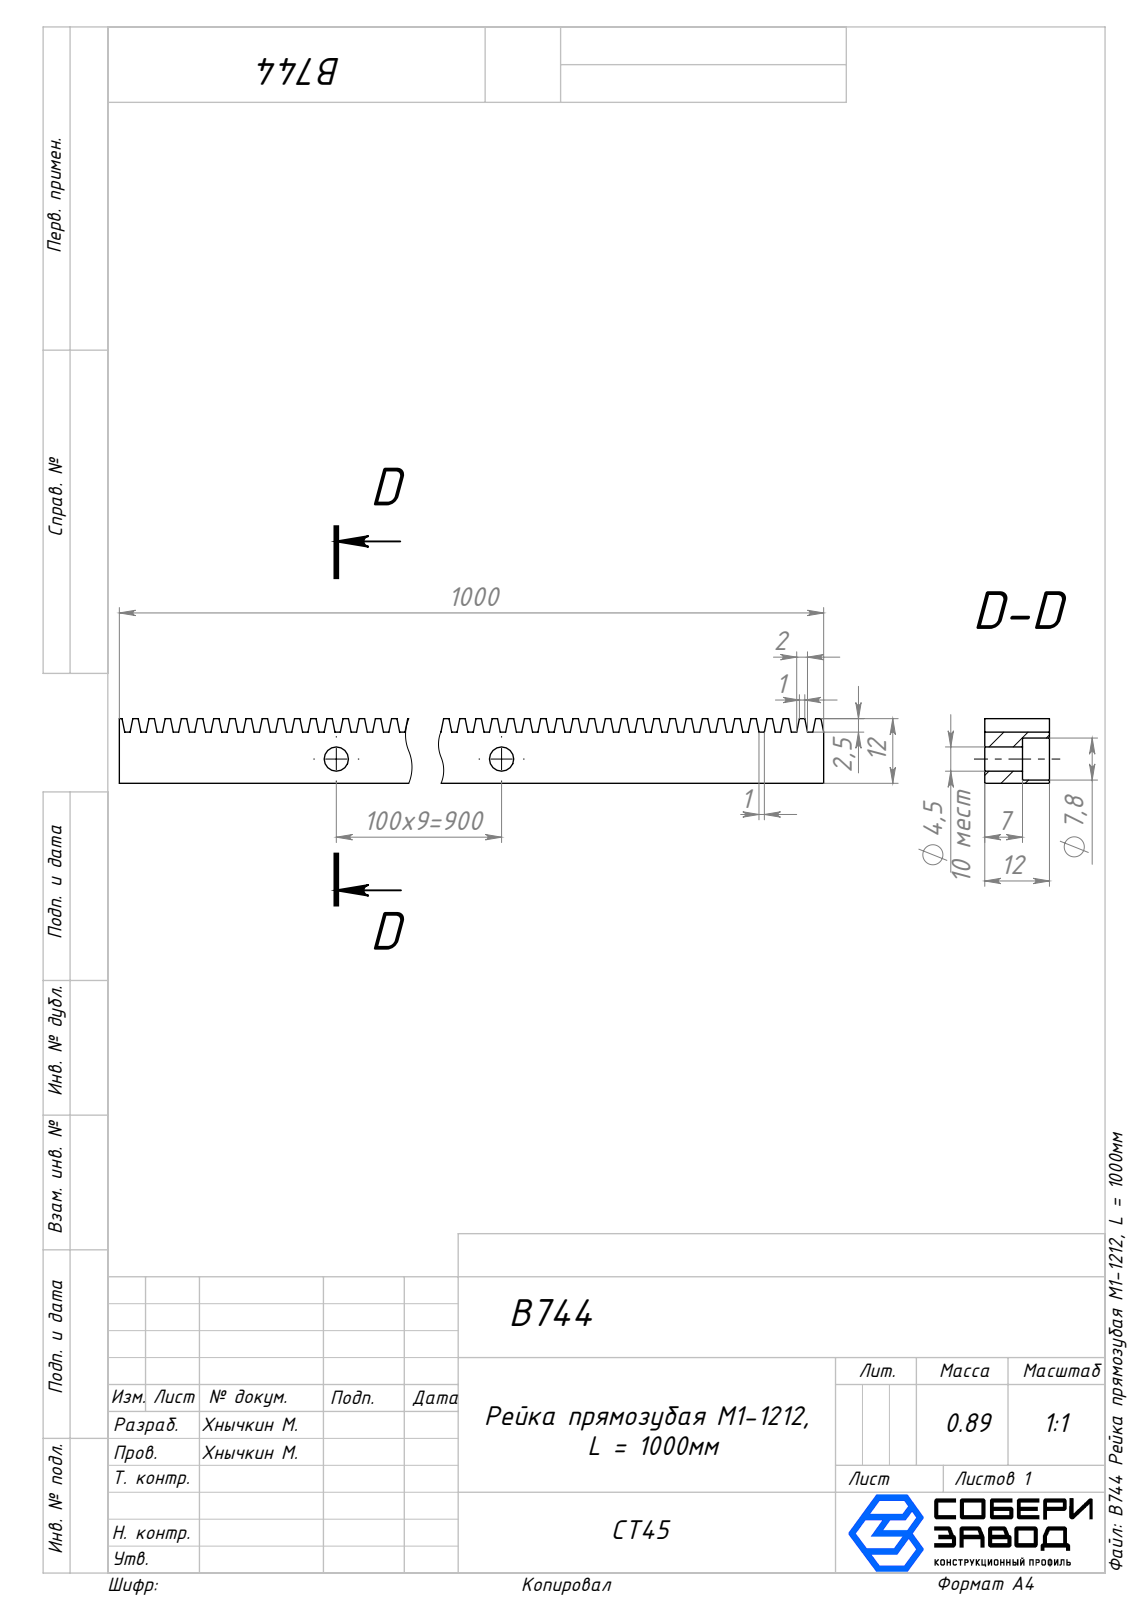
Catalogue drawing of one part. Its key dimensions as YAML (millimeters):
part_name: "B744 Рейка прямозубая M1-1212, L = 1000мм"
step_written_by: "SolidWorks 2025 (AUTOMOTIVE_DESIGN)"
units: millimeters
bodies: {solids: 1, faces: 1389, planar: 1349, cylindrical: 40, other: 0}
overall_size: [1000, 12, 12]
volume: 125505
surface_area: 64060
round_holes:
  - {diameter: 4.5, count: 10}
  - {diameter: 7.8, count: 10}
face_to_face_distances: [12, 9.5, 2.5, 2.94, 8.83, 5.89, 17.66, 11.77, 14.72, 20.6]
hole_center_spacings: [100, 200, 99.97, 300, 299.92, 399.89, 400, 500]
